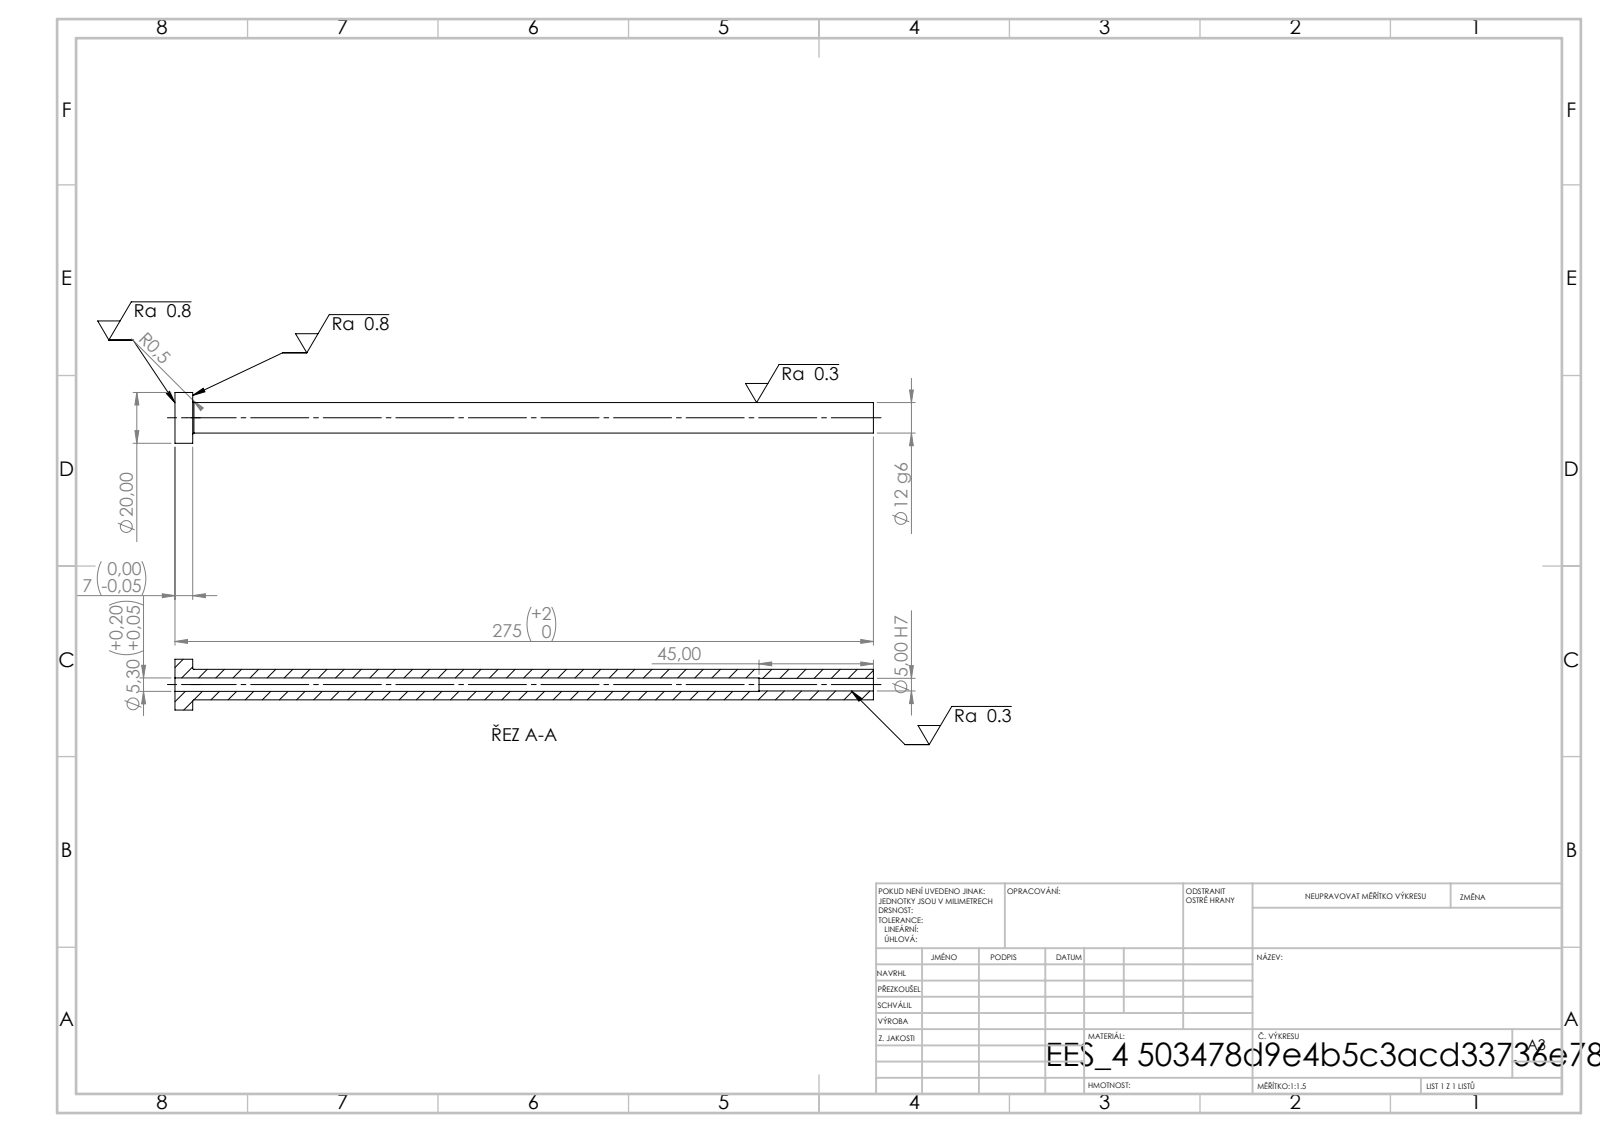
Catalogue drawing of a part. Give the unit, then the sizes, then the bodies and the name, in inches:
Units: inches
Overall size (bounding box): 10.827 × 0.787 × 0.787
Round holes (diameter × count): ⌀0.197 ×1, ⌀0.209 ×1
Round bosses / shafts (diameter × count): ⌀0.787 ×1, ⌀0.472 ×1
Main face-to-face distances: 0.276, 10.827, 10.551, 9.055, 8.78, 1.772
Volume: 1.62 in³ · Surface area: 24.27 in²
Bodies: 1 solid, 14 faces (4 planar, 8 cylindrical, 2 other)
STEP written by: SolidWorks 2019 (CONFIG_CONTROL_DESIGN)
